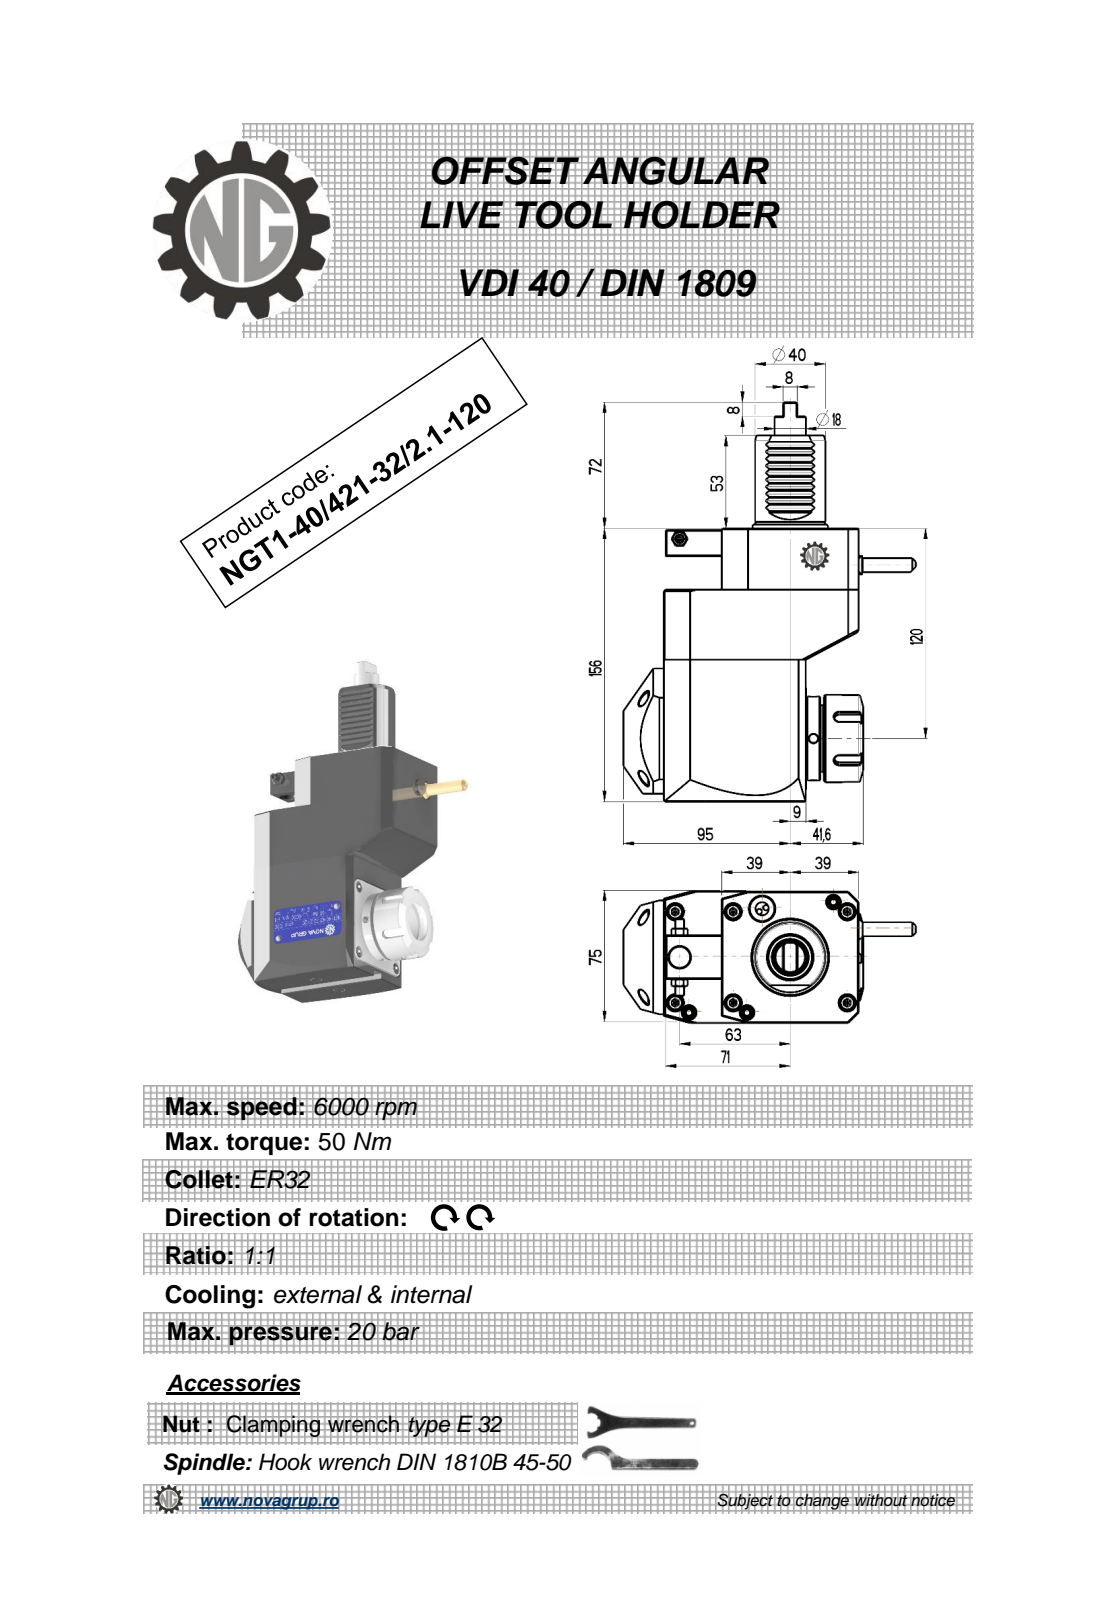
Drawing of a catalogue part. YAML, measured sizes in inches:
part_name: "NGT1_40_421_32_2_1_120"
step_written_by: "PRO/ENGINEER BY PARAMETRIC TECHNOLOGY CORPORATION, 2010280 (CONFIG_CONTROL_DESIGN)"
units: inches
bodies: {solids: 1, faces: 427, planar: 211, cylindrical: 89, other: 127}
overall_size: [8.976, 6.555, 3.016]
volume: 72.92
surface_area: 136.2
round_holes:
  - {diameter: 0.197, count: 3}
  - {diameter: 0.118, count: 1}
  - {diameter: 0.165, count: 1}
  - {diameter: 0.374, count: 1}
  - {diameter: 0.472, count: 1}
  - {diameter: 1.063, count: 1}
round_bosses_or_shafts:
  - {diameter: 1.969, count: 1}
  - {diameter: 1.89, count: 1}
  - {diameter: 1.614, count: 1}
  - {diameter: 1.575, count: 1}
  - {diameter: 0.701, count: 1}
  - {diameter: 0.441, count: 1}
  - {diameter: 0.353, count: 1}
  - {diameter: 0.315, count: 1}
partial_cylinders:
  - {radius: 0.01, count: 12}
  - {radius: 0.012, count: 10}
  - {radius: 0.009, count: 6}
  - {radius: 0.118, count: 5}
  - {radius: 0.031, count: 2}
  - {radius: 0.02, count: 1}
  - {radius: 1.575, count: 1}
face_to_face_distances: [2.953, 6.142, 4.37, 1.378, 4.764, 3.189, 1.181, 1.299, 1.89, 3.071]
hole_center_spacings: [0.824, 3.002, 3.948, 4.429, 5.4]
